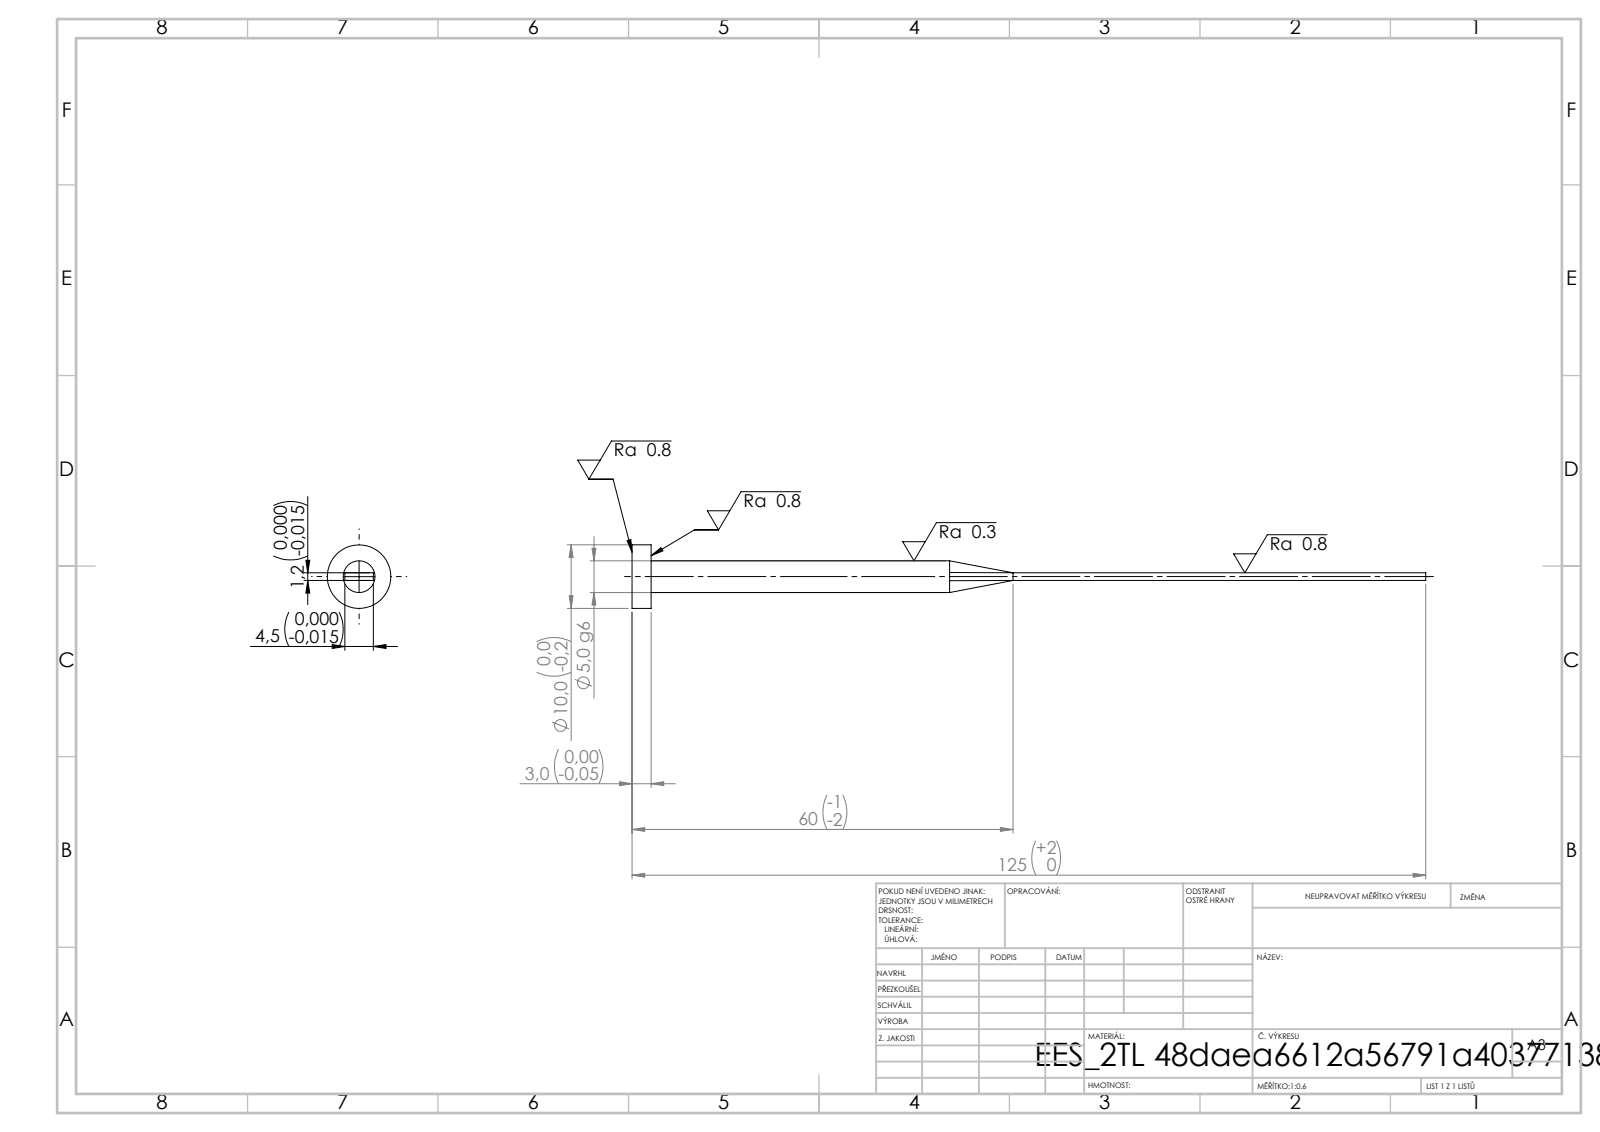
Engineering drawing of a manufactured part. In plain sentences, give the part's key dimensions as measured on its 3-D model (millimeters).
Its 3-D file was written by "SolidWorks 2019 (CONFIG_CONTROL_DESIGN)". It is 1 solid with 15 faces: 7 planar, 4 cylindrical and 4 other. Overall it measures 125 by 10 by 10 millimeters. Its volume is 1 629 cubic millimeters and its surface area 1 848 square millimeters. Round bosses or shafts: 1 of diameter 10, 1 of diameter 5. The main face-to-face distances are 1.2, 4.5, 3, 125, 122.
